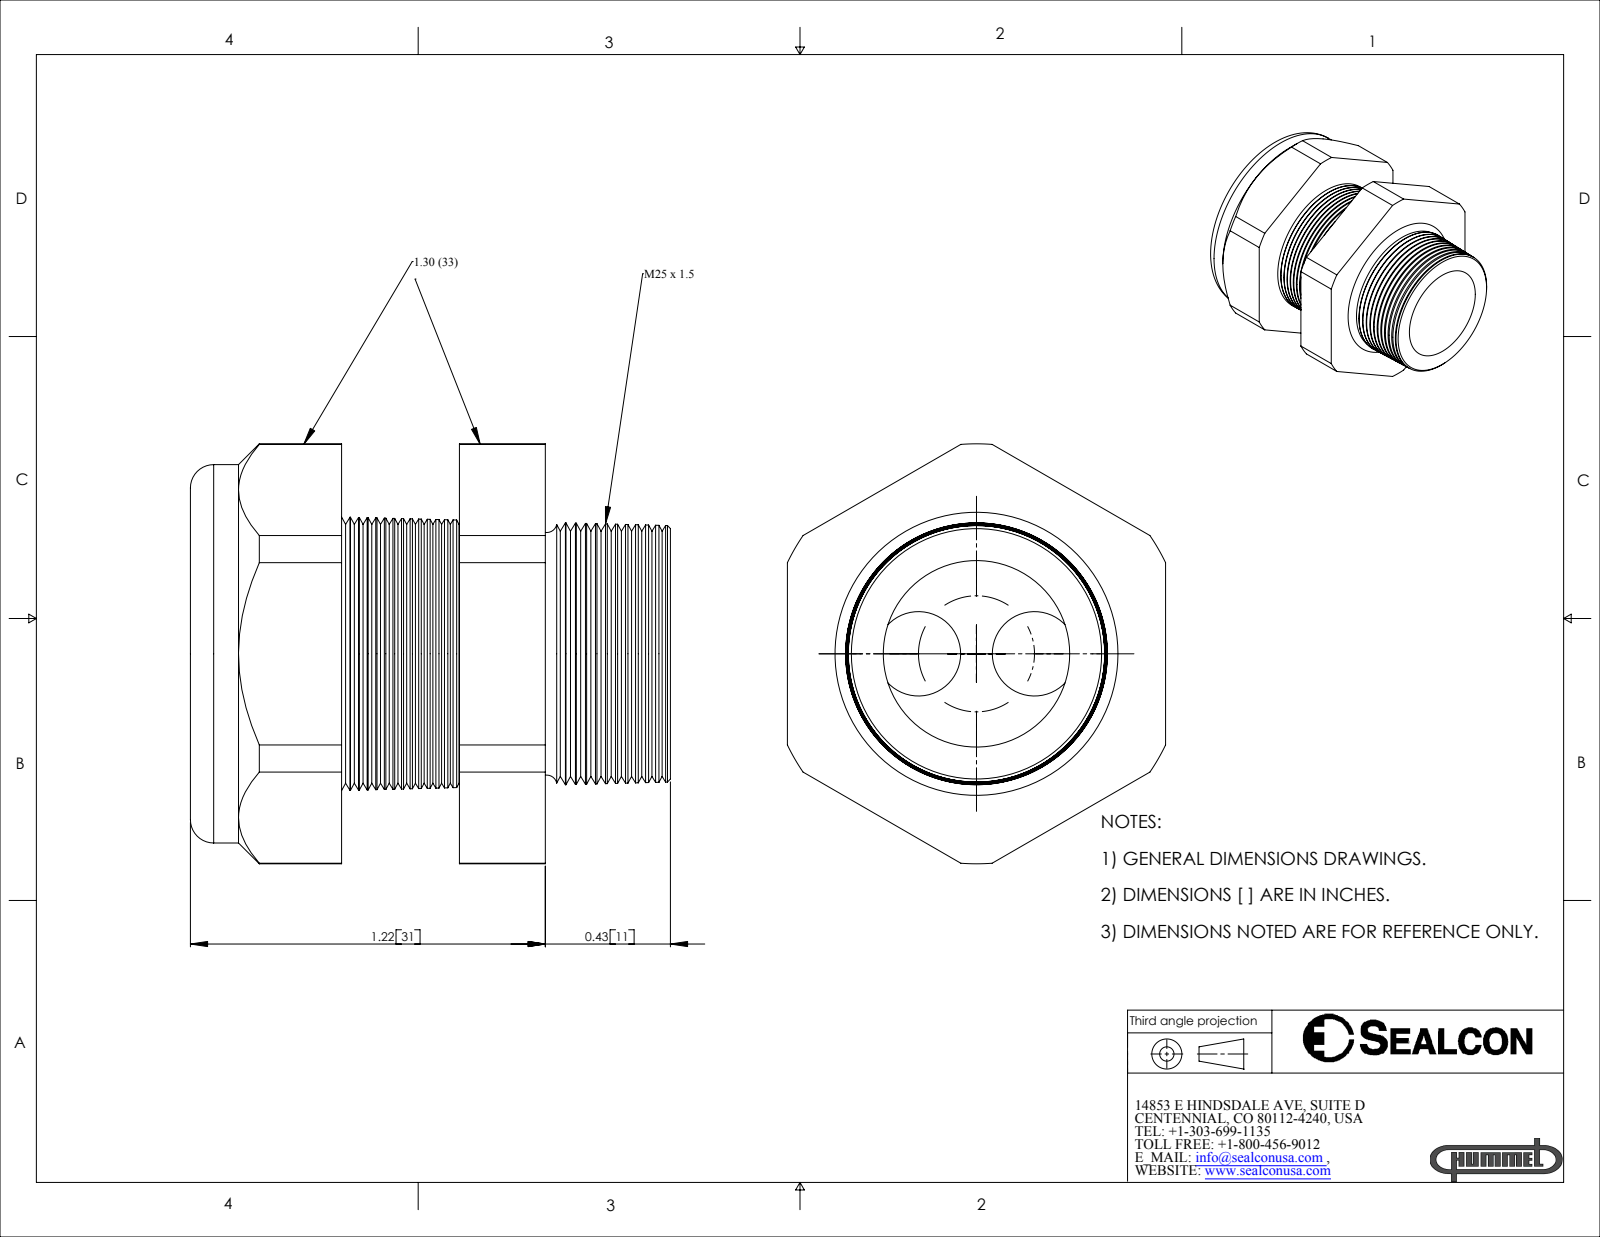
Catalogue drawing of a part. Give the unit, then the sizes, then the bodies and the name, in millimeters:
Units: millimetres
Overall size (bounding box): 41.9 × 36.7 × 33
Round holes (diameter × count): ⌀7.4 ×2, ⌀17.5 ×1, ⌀18 ×1
Round bosses / shafts (diameter × count): ⌀33 ×1
Partial cylindrical surfaces — rounded edges, fillets, slot ends (radius × count): R18.3 ×1
Main face-to-face distances: 33, 10.3, 17.8, 7.5, 13.2, 23.5, 31, 8.9, 4.3, 14.6
Hole centre spacings: 5.1, 10.1
Volume: 18 800 mm³ · Surface area: 10 900 mm²
Bodies: 2 solids, 210 faces (20 planar, 24 cylindrical, 166 other)
Part name (STEP PRODUCT): CD25M9-GY
STEP written by: SolidWorks 2007 (CONFIG_CONTROL_DESIGN)
